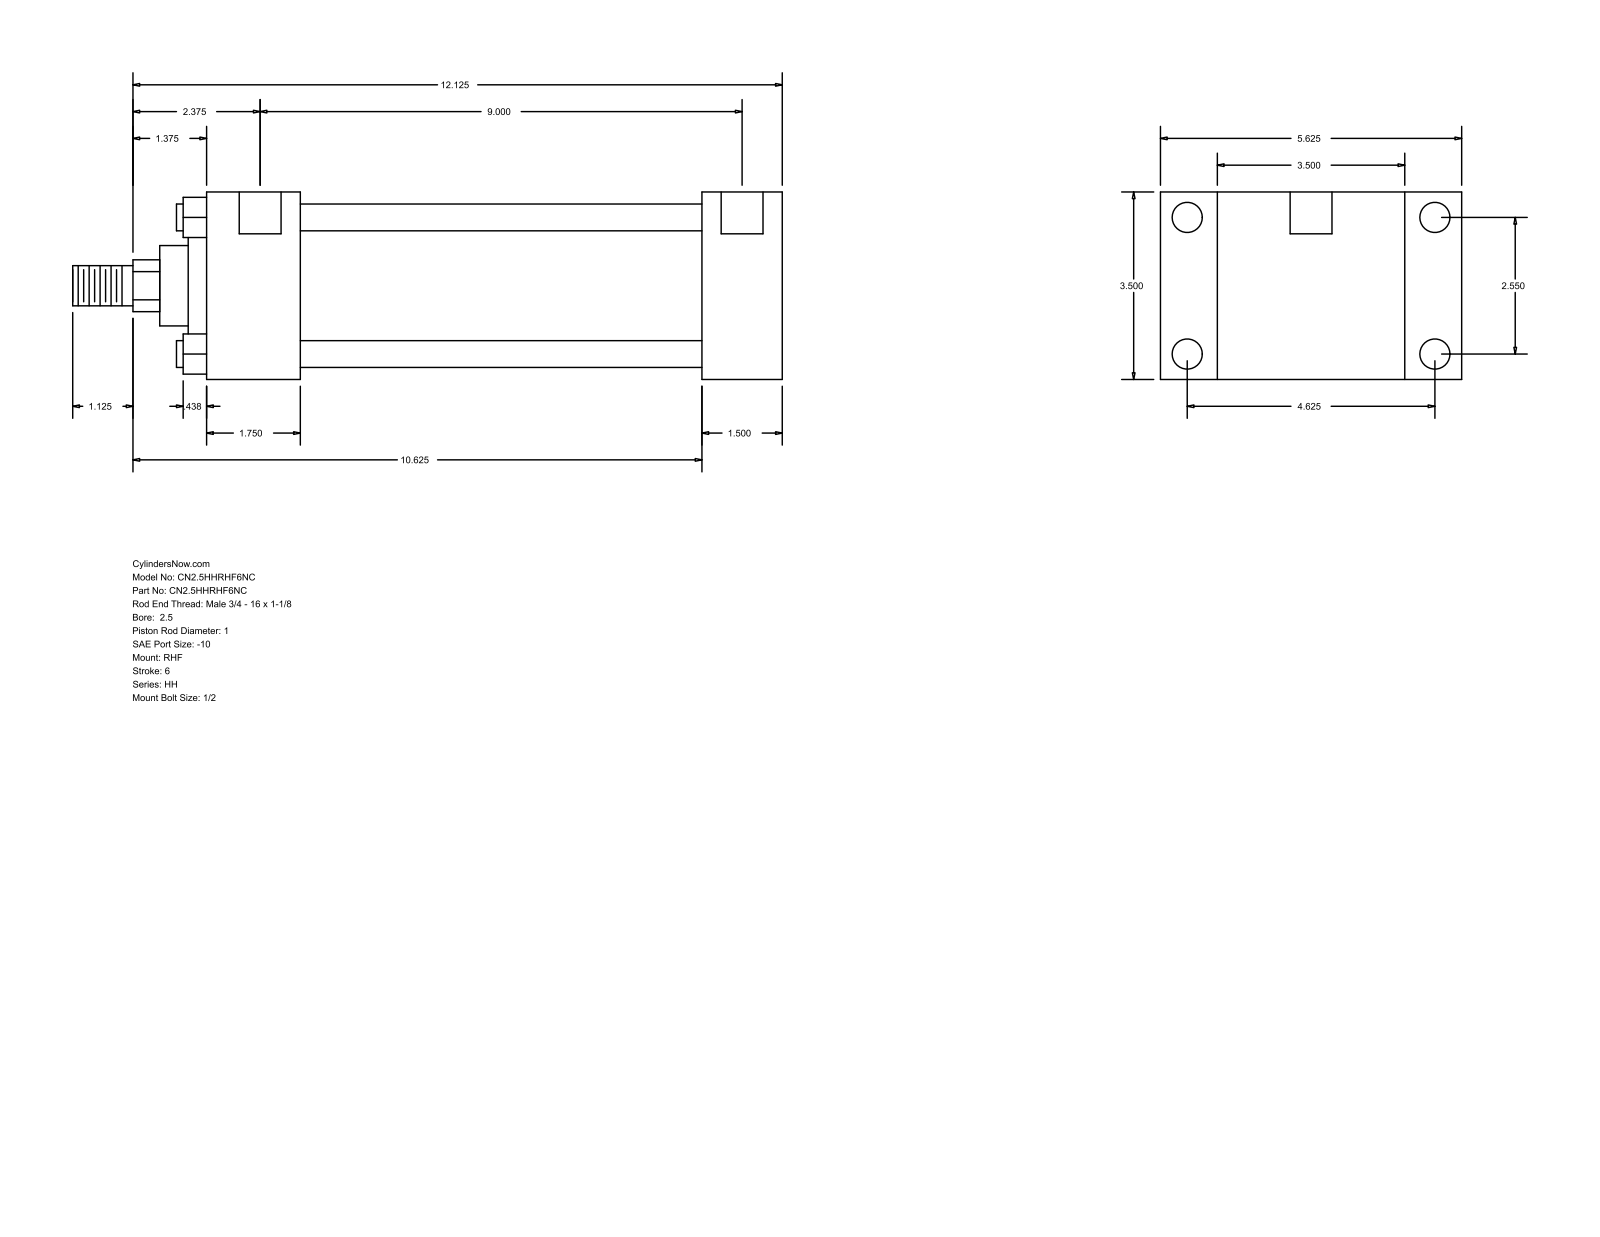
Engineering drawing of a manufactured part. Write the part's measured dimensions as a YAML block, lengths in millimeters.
part_name: "HH_RHF__0250_1"
step_written_by: "GSSL Pune (CONFIG_CONTROL_DESIGN)"
units: millimeters
bodies: {solids: 0, faces: 90, planar: 61, cylindrical: 29, other: 0}
overall_size: [336.55, 142.88, 88.9]
round_holes:
  - {diameter: 5.56, count: 4}
  - {diameter: 14.3, count: 4}
  - {diameter: 19.84, count: 2}
round_bosses_or_shafts:
  - {diameter: 12.7, count: 4}
  - {diameter: 73.03, count: 1}
  - {diameter: 60.33, count: 1}
  - {diameter: 38.1, count: 1}
  - {diameter: 25.4, count: 1}
  - {diameter: 19.05, count: 1}
partial_cylinders:
  - {radius: 12.29, count: 1}
face_to_face_distances: [88.9, 38.1, 26.99, 115.89, 234.96, 273.06, 142.88, 44.46, 190.5, 228.6]
hole_center_spacings: [64.76, 117.48, 134.15, 231.77, 1.58, 1.59, 228.6, 230.18]
